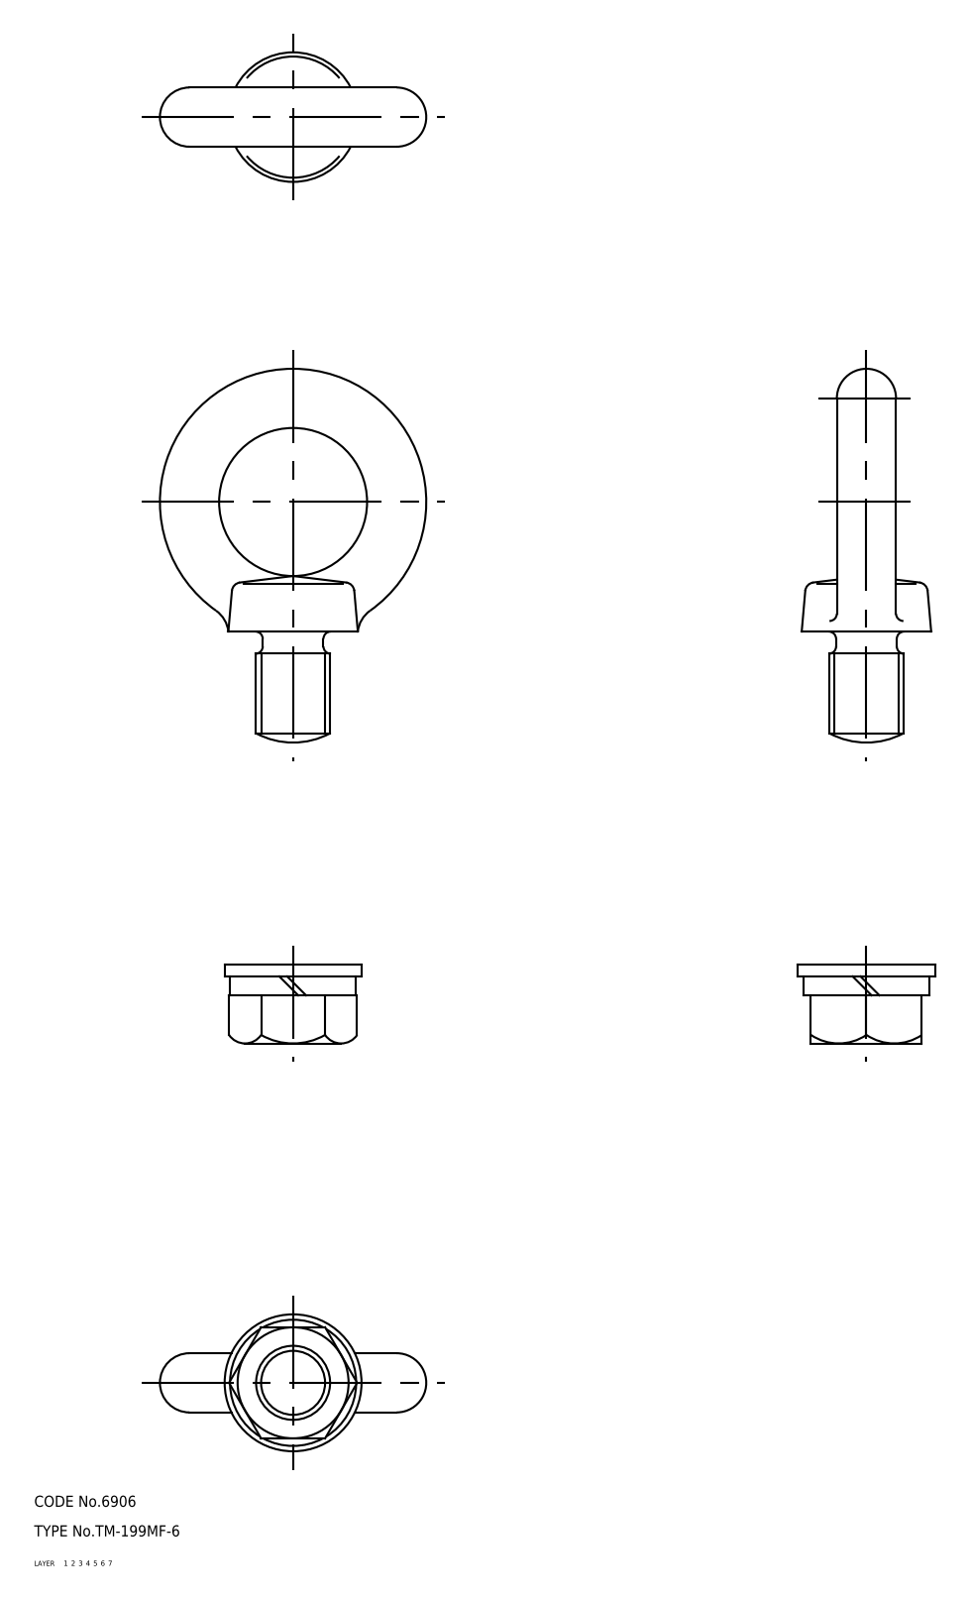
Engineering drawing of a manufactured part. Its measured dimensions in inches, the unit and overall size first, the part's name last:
Units: inches
Overall size (bounding box): 3.976 × 2.835 × 1.457
Round holes (diameter × count): ⌀0.787 ×1
Round bosses / shafts (diameter × count): ⌀1.457 ×1, ⌀1.343 ×1
Main face-to-face distances: 0.126, 0.201, 0.327, 1.181, 0.512, 0.713, 0.839
Volume: 3.816 in³ · Surface area: 29.59 in²
Bodies: 4 solids, 56 faces (13 planar, 12 cylindrical, 31 other)
Part name (STEP PRODUCT): TM_199MF_6
STEP written by: SolidWorks 2003240 (AUTOMOTIVE_DESIGN)
